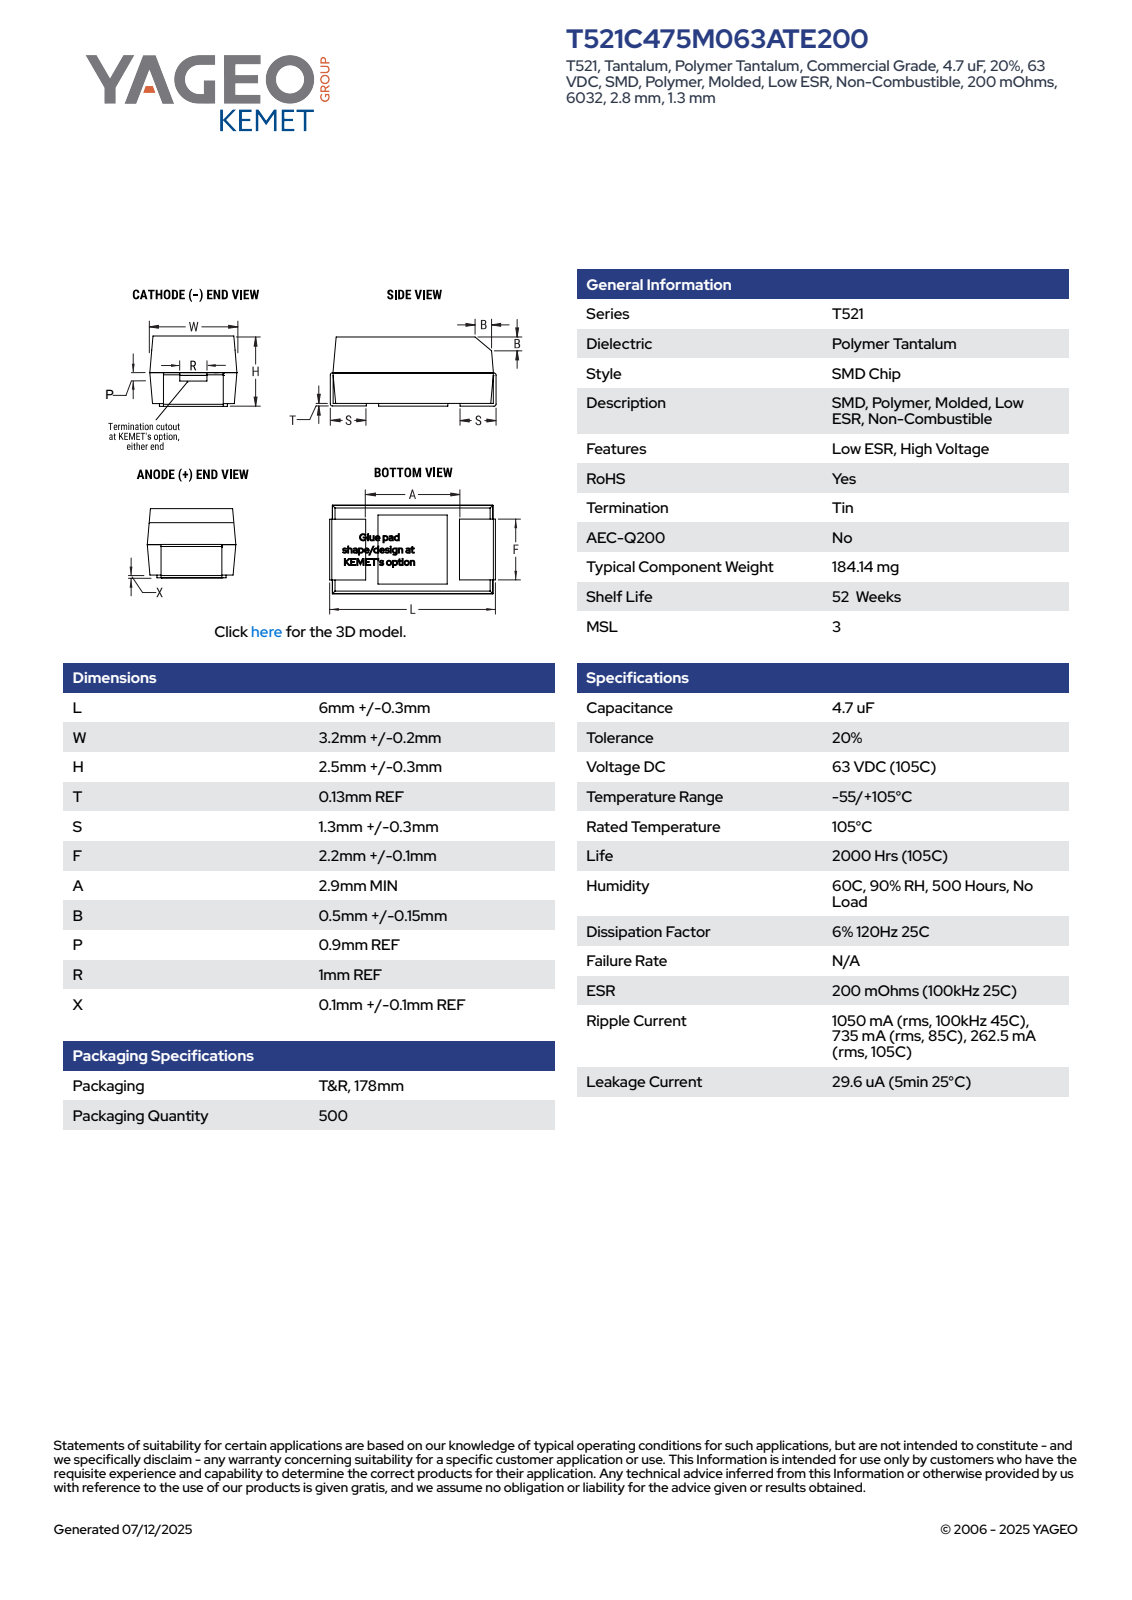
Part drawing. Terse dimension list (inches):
name: CTSM_TCM2NKKO_6032_L6.3W3.4H2.8T0.13S1.3F2.3A2.9B0.65P0.9R1X0.1
written by: SolidWorks 2021 (AUTOMOTIVE_DESIGN)
unit: in
bodies: 4 solids, 100 faces (95 planar, 5 cylindrical, 0 other)
size: 0.248 × 0.134 × 0.111
volume: 0.003 in³; area: 0.15 in²
rounds: 4× R0.004
face distances: 0.133, 0.11, 0.106, 0.111, 0.243, 0.248, 0.238, 0.051, 0.091, 0.046
